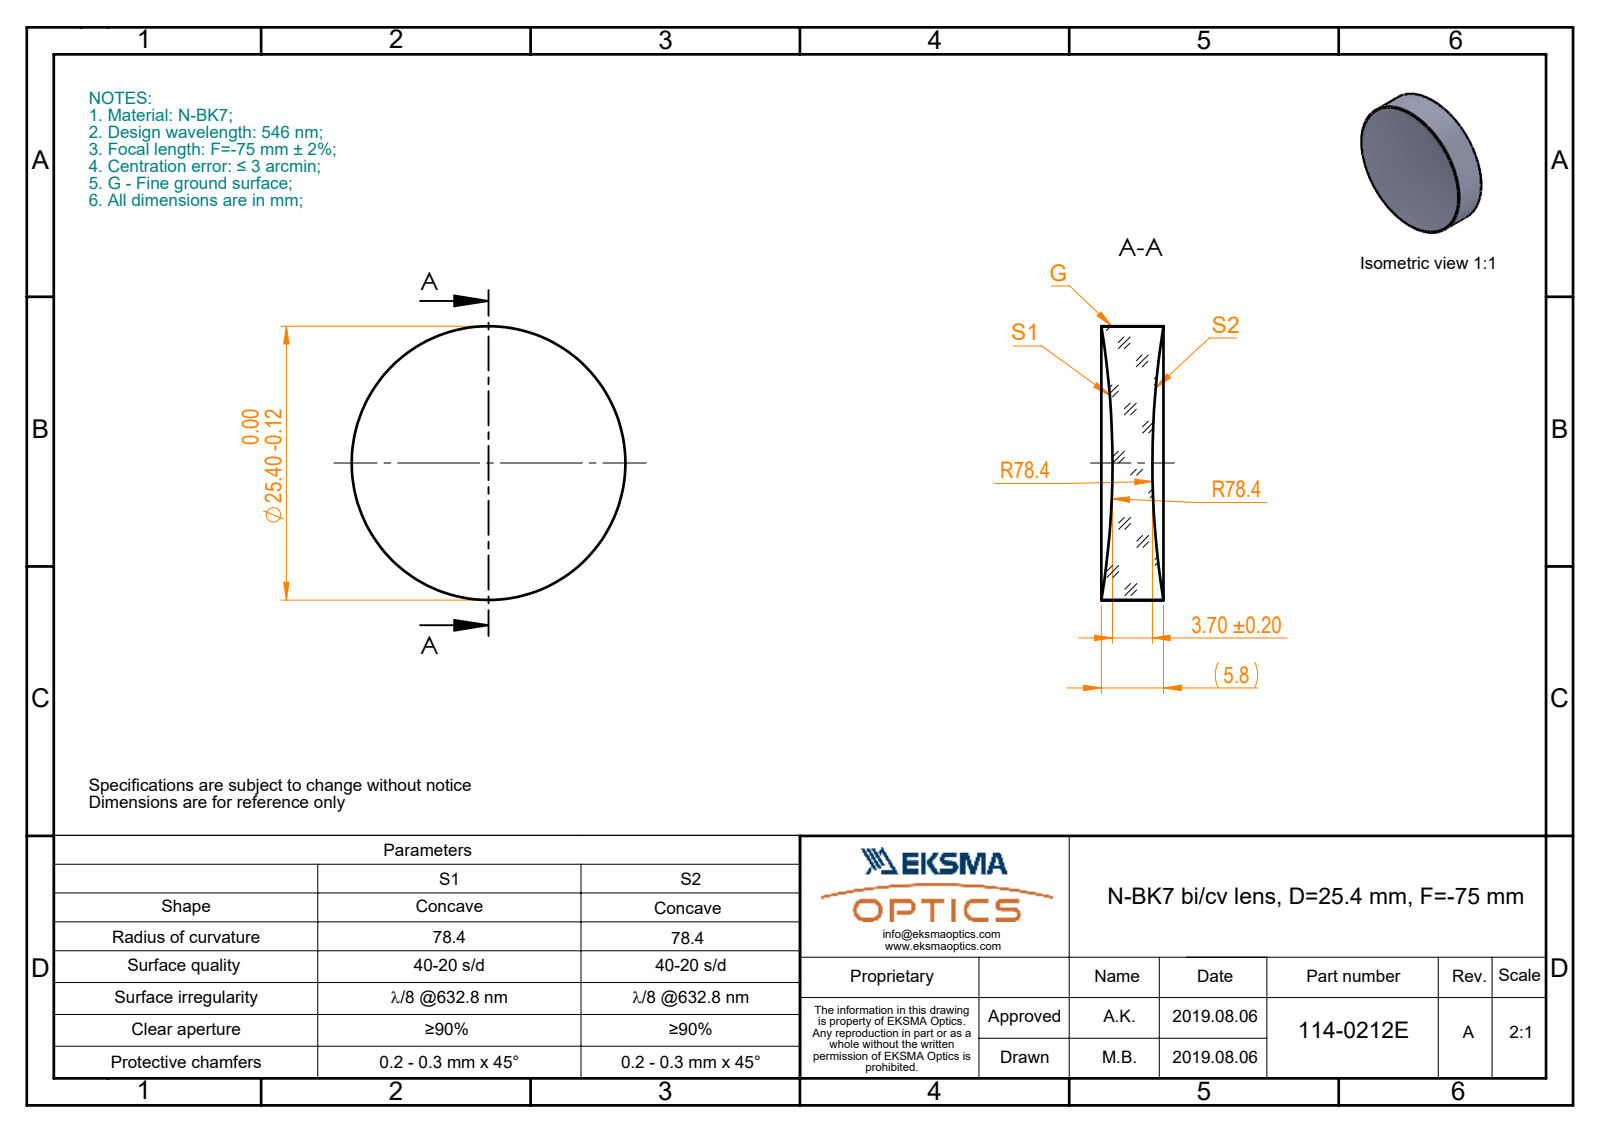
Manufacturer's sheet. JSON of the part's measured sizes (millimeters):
{"part_name": "114-0212E BK7 bi-cv 25.4 F-75", "step_written_by": "SolidWorks 2017 (CONFIG_CONTROL_DESIGN)", "units": "millimeters", "bodies": {"solids": 1, "faces": 6, "planar": 0, "cylindrical": 2, "other": 4}, "overall_size": [25.4, 25.4, 5.77], "volume_mm3": 2398, "surface_area_mm2": 1481, "round_bosses_or_shafts": [[25.4, 1]]}
